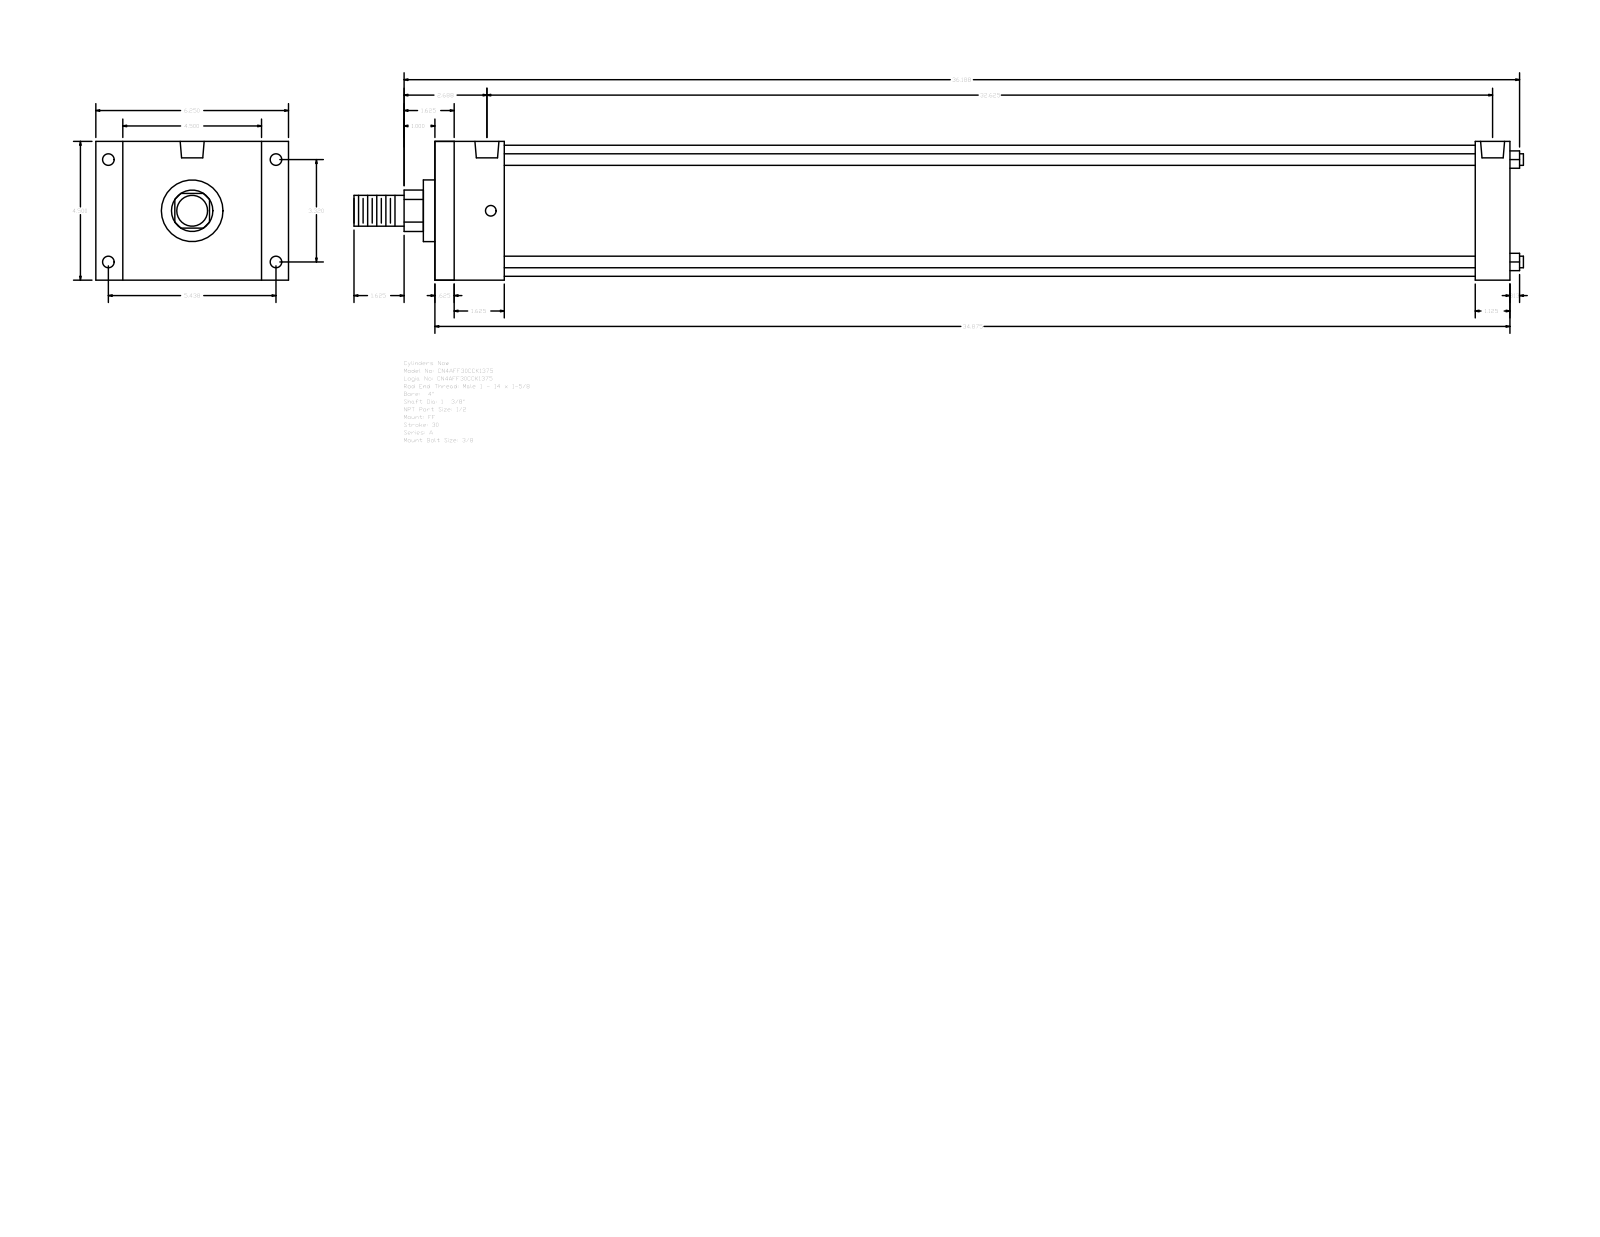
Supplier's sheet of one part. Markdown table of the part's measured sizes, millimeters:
| quantity | value |
| --- | --- |
| part name | A_FF__0400_1.375 |
| STEP written by | GSSL Pune (CONFIG_CONTROL_DESIGN) |
| units | millimeters |
| bodies | 0 solids, 92 faces (64 planar, 28 cylindrical, 0 other) |
| overall size | 963.61 × 158.75 × 114.3 |
| round holes (diameter × count) | 8.73 × 4, 9.53 × 4, 19.77 × 2 |
| round bosses / shafts (diameter × count) | 9.53 × 4, 107.95 × 1, 50.8 × 1, 34.92 × 1, 25.4 × 1 |
| partial cylindrical surfaces (radius × count) | 17.06 × 1 |
| main face-to-face distances | 114.3, 885.83, 15.87, 869.96, 57.15, 28.58, 22.23, 136.53, 857.25, 841.38 |
| hole center spacings | 3.18, 84.32, 138.12, 161.82, 822.32, 825.5, 828.68 |
